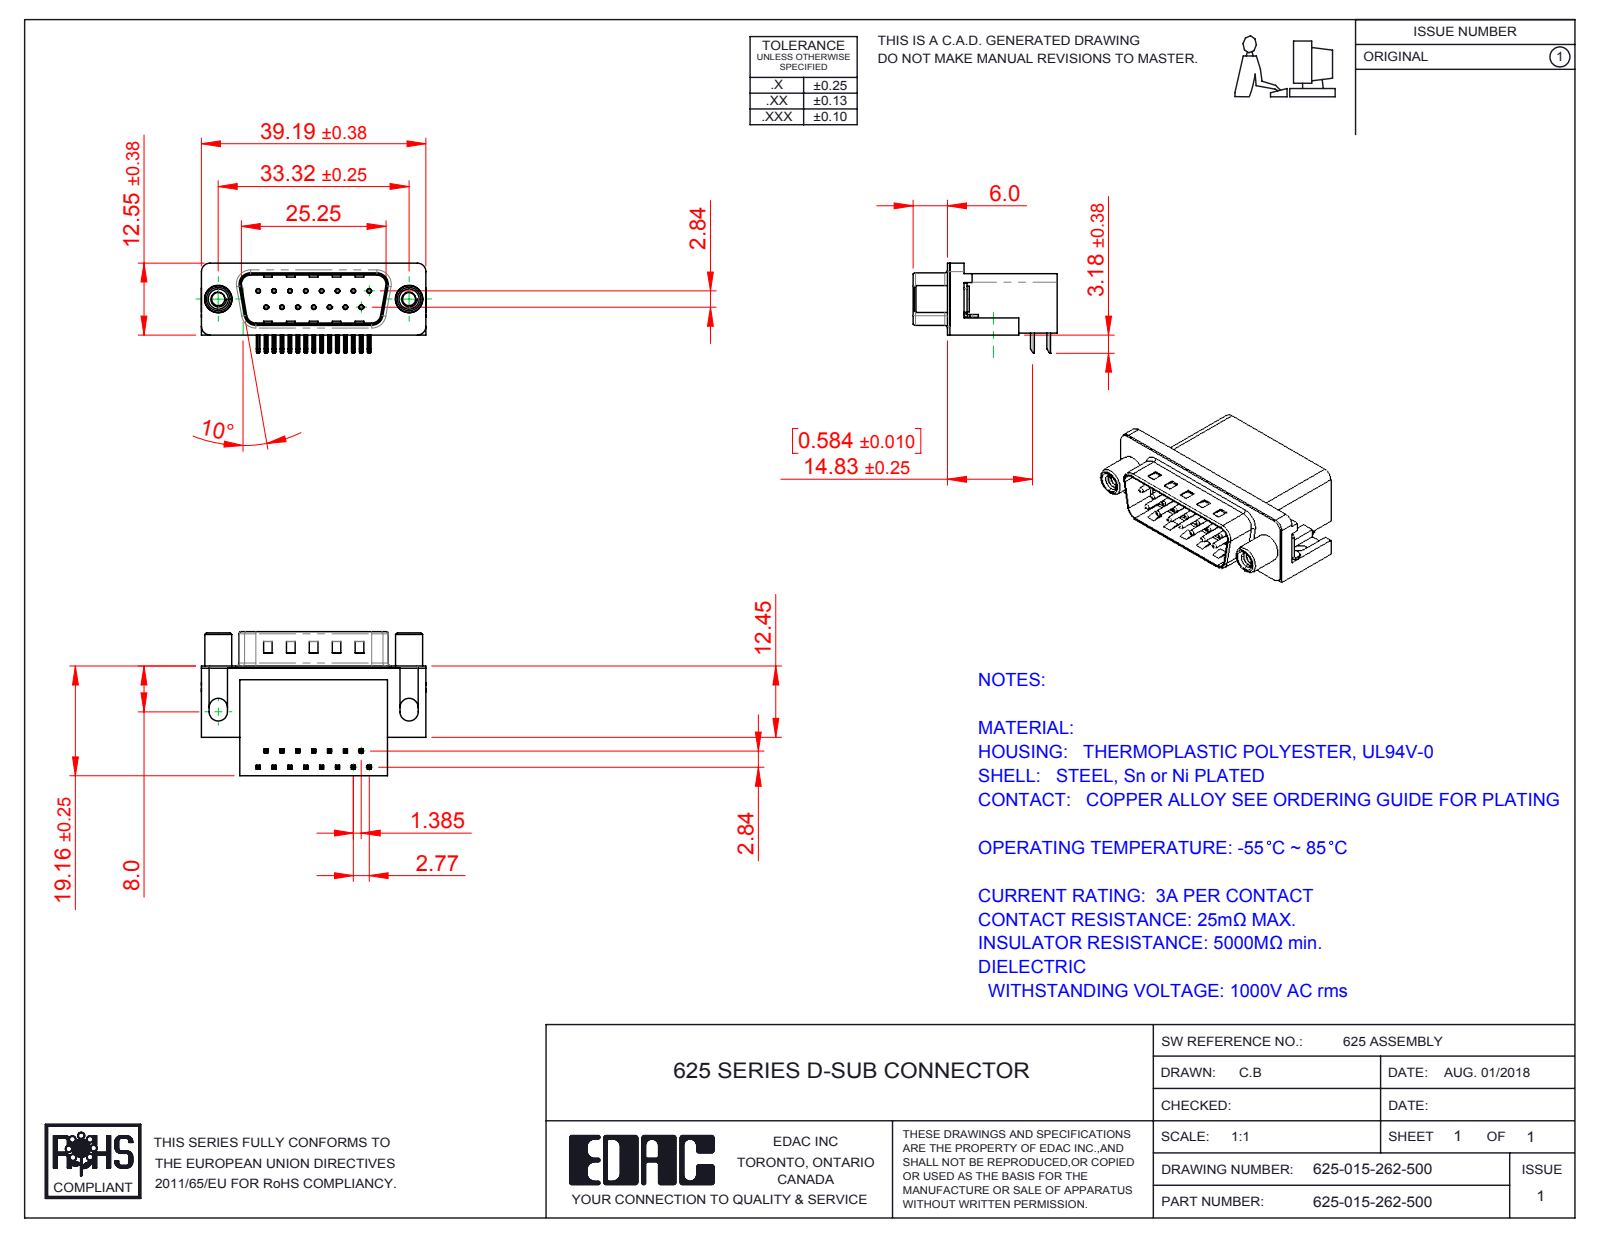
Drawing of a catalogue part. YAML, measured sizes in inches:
part_name: "625 Round Threaded Standoff; 625 Housing_15 Socket; 625 Non Board Mount; 625 Contact Top (+3 more)"
step_written_by: "SolidWorks 2016 (CONFIG_CONTROL_DESIGN)"
units: inches
bodies: {solids: 21, faces: 1471, planar: 887, cylindrical: 451, other: 133}
overall_size: [1.544, 0.991, 0.619]
volume: 0.385
surface_area: 10.06
round_holes:
  - {diameter: 0.014, count: 15}
  - {diameter: 0.031, count: 15}
  - {diameter: 0.091, count: 2}
  - {diameter: 0.122, count: 2}
  - {diameter: 0.157, count: 2}
  - {diameter: 0.189, count: 2}
  - {diameter: 0.197, count: 2}
round_bosses_or_shafts:
  - {diameter: 0.03, count: 15}
  - {diameter: 0.193, count: 2}
  - {diameter: 0.185, count: 2}
  - {diameter: 0.177, count: 2}
  - {diameter: 0.152, count: 2}
partial_cylinders:
  - {radius: 0.01, count: 60}
  - {radius: 0.005, count: 30}
  - {radius: 0.039, count: 16}
  - {radius: 0.02, count: 9}
  - {radius: 0.063, count: 8}
  - {radius: 0.059, count: 6}
  - {radius: 0.035, count: 4}
  - {radius: 0.079, count: 4}
face_to_face_distances: [0.016, 0.407, 0.739, 0.083, 0.412, 0.067, 0.428, 0.754, 0.345, 0.64]
hole_center_spacings: [0.124, 0.109, 0.218, 0.327, 0.436, 0.198, 0.198, 0.294]
